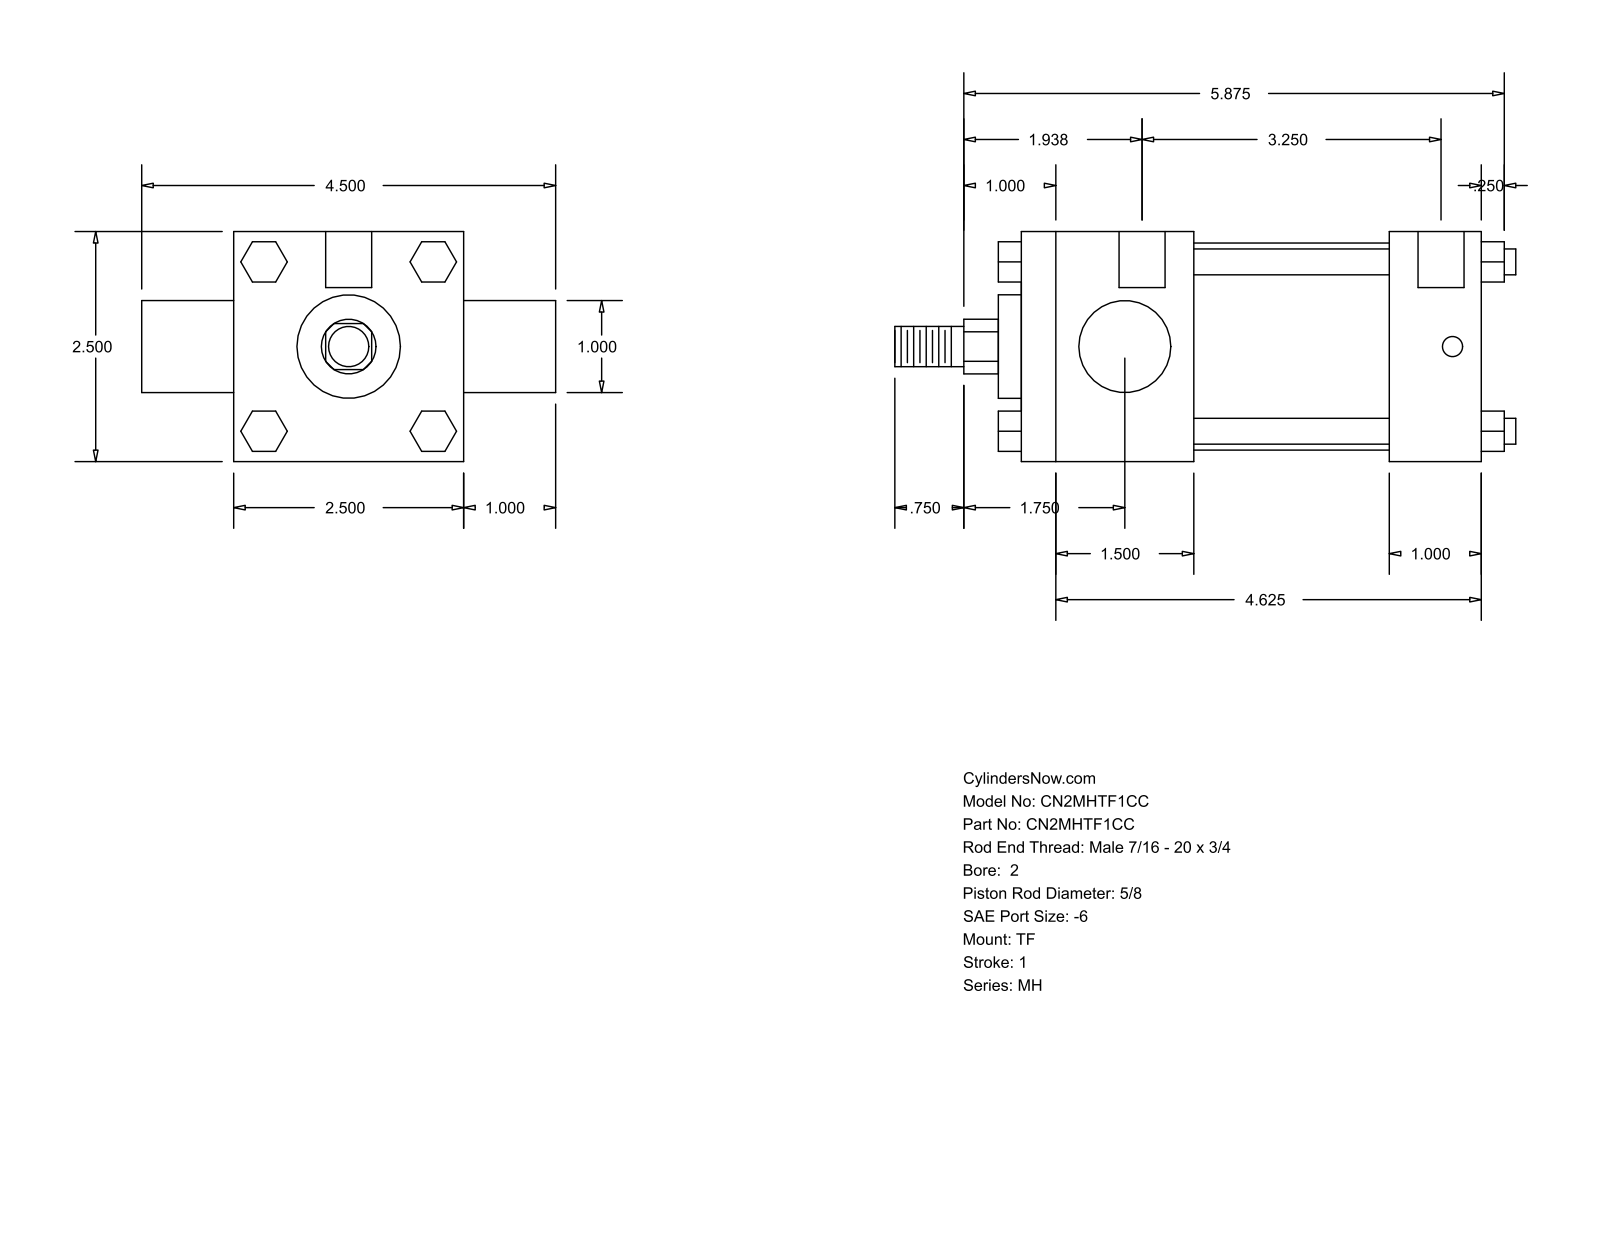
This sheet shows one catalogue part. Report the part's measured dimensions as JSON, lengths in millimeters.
{"part_name": "MH_TF__0200_0.625", "step_written_by": "GSSL Pune (CONFIG_CONTROL_DESIGN)", "units": "millimeters", "bodies": {"solids": 0, "faces": 120, "planar": 92, "cylindrical": 28, "other": 0}, "overall_size": [171.45, 114.3, 63.5], "round_holes": [[5.56, 3], [12.7, 2]], "round_bosses_or_shafts": [[7.14, 4], [57.15, 1], [28.57, 1], [25.4, 1], [15.88, 1], [11.11, 1]], "partial_cylinders_radius": [[7.54, 1]], "face_to_face_distances": [63.5, 127, 53.97, 47.62, 101.59, 79.38, 25.41, 25.4, 88.9, 6.35], "hole_center_spacings": [3.18, 4.76, 82.55, 85.73, 87.31, 90.49]}
